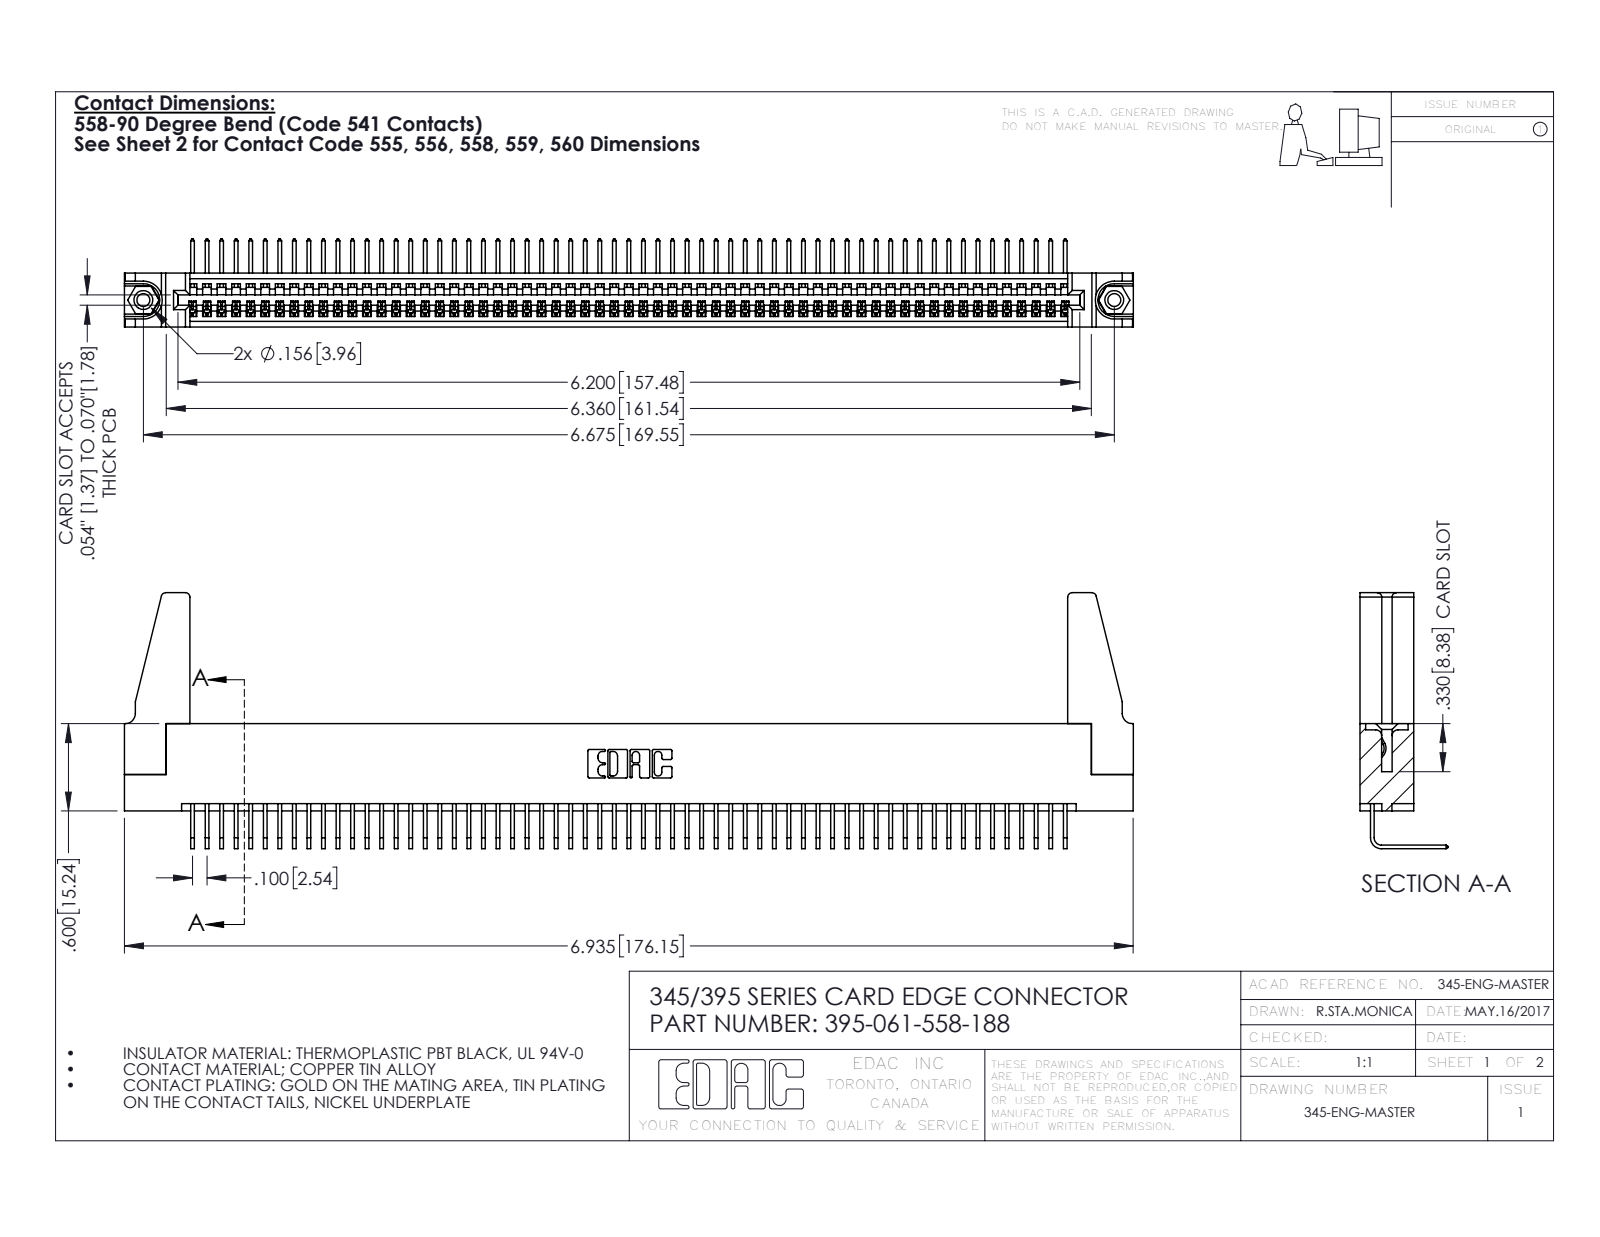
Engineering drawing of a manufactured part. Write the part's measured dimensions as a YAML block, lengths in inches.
part_name: "395-061-558-188; 345-220-078_345-220-088; 345-292-001_558 Tail - 2; 345 Part_Flush Mounting Lugs - 0.156 Dia-TH (+1 more)"
step_written_by: "SolidWorks 2016 (CONFIG_CONTROL_DESIGN)"
units: inches
bodies: {solids: 66, faces: 3910, planar: 2714, cylindrical: 1180, other: 16}
overall_size: [6.936, 1.759, 0.605]
volume: 1.242
surface_area: 42.31
round_holes:
  - {diameter: 0.089, count: 2}
  - {diameter: 0.125, count: 2}
  - {diameter: 0.156, count: 2}
  - {diameter: 0.064, count: 1}
round_bosses_or_shafts:
  - {diameter: 0.155, count: 2}
partial_cylinders:
  - {radius: 0.006, count: 122}
  - {radius: 0.01, count: 22}
  - {radius: 0.03, count: 8}
  - {radius: 0.007, count: 6}
  - {radius: 0.031, count: 6}
  - {radius: 0.026, count: 3}
  - {radius: 0.031, count: 2}
  - {radius: 0.04, count: 2}
face_to_face_distances: [0.072, 0.298, 0.37, 0.2, 0.098, 0.272, 0.025, 0.225, 0.149, 0.072]
hole_center_spacings: [0.27, 6.439, 6.675]
